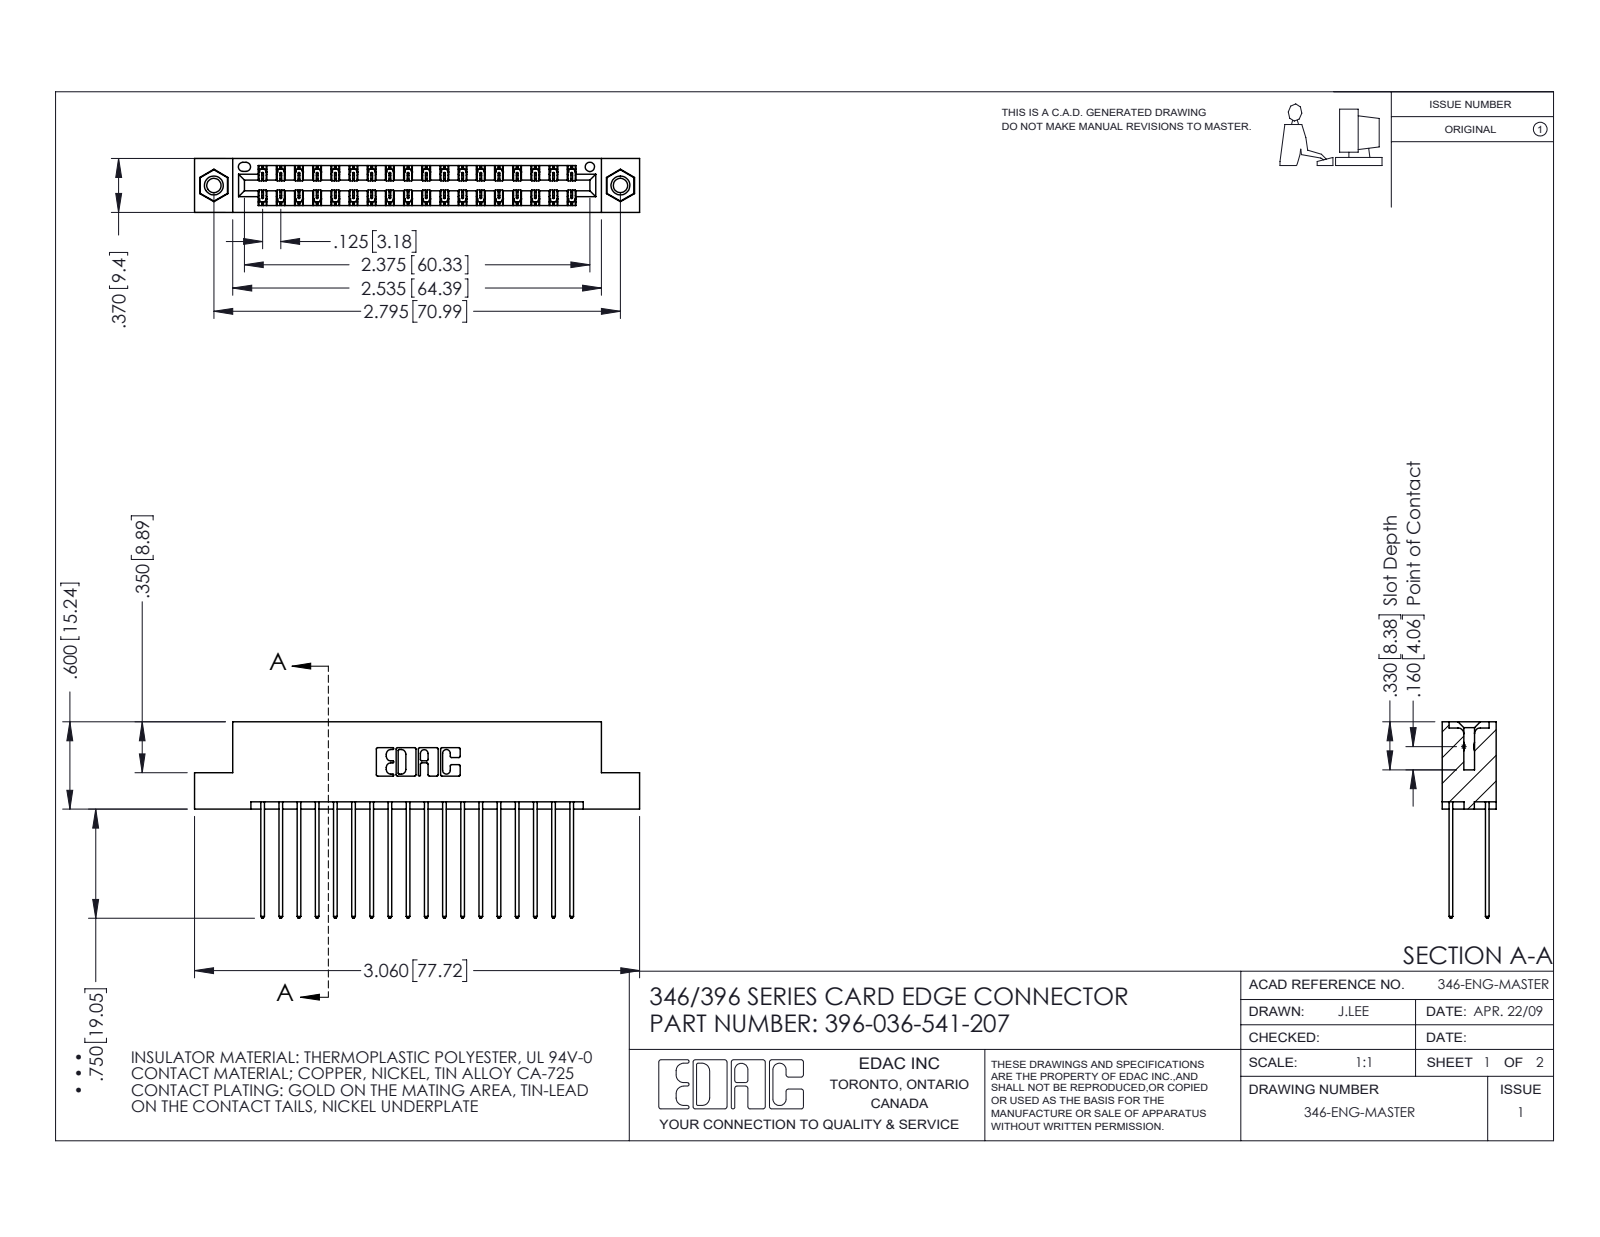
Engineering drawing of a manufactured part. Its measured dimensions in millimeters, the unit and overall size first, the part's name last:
Units: millimetres
Overall size (bounding box): 77.7 × 34.3 × 9.4
Round holes (diameter × count): ⌀2.5 ×2, ⌀3.2 ×2, ⌀4 ×2, ⌀1.6 ×1
Round bosses / shafts (diameter × count): ⌀3.9 ×2
Partial cylindrical surfaces — rounded edges, fillets, slot ends (radius × count): R0.2 ×54, R0.3 ×36, R0.3 ×22, R0.2 ×6, R0.8 ×6, R0.7 ×3, R0.4 ×2, R0.6 ×2
Main face-to-face distances: 1.2, 8.2, 6.4, 1.8, 7.6, 0.6, 9.4, 7, 3.8, 5.6
Hole centre spacings: 6.2, 65.7, 71
Volume: 7 590 mm³ · Surface area: 11 070 mm²
Bodies: 39 solids, 2054 faces (1368 planar, 670 cylindrical, 16 other)
Part name (STEP PRODUCT): 345-250-001_345-250-005-103; 396-036-541-207; 345-292-001_345-293-141; 346 Part_Flush Mounting Lugs - 0.156 Dia-TI
STEP written by: SolidWorks 2016 (CONFIG_CONTROL_DESIGN)
